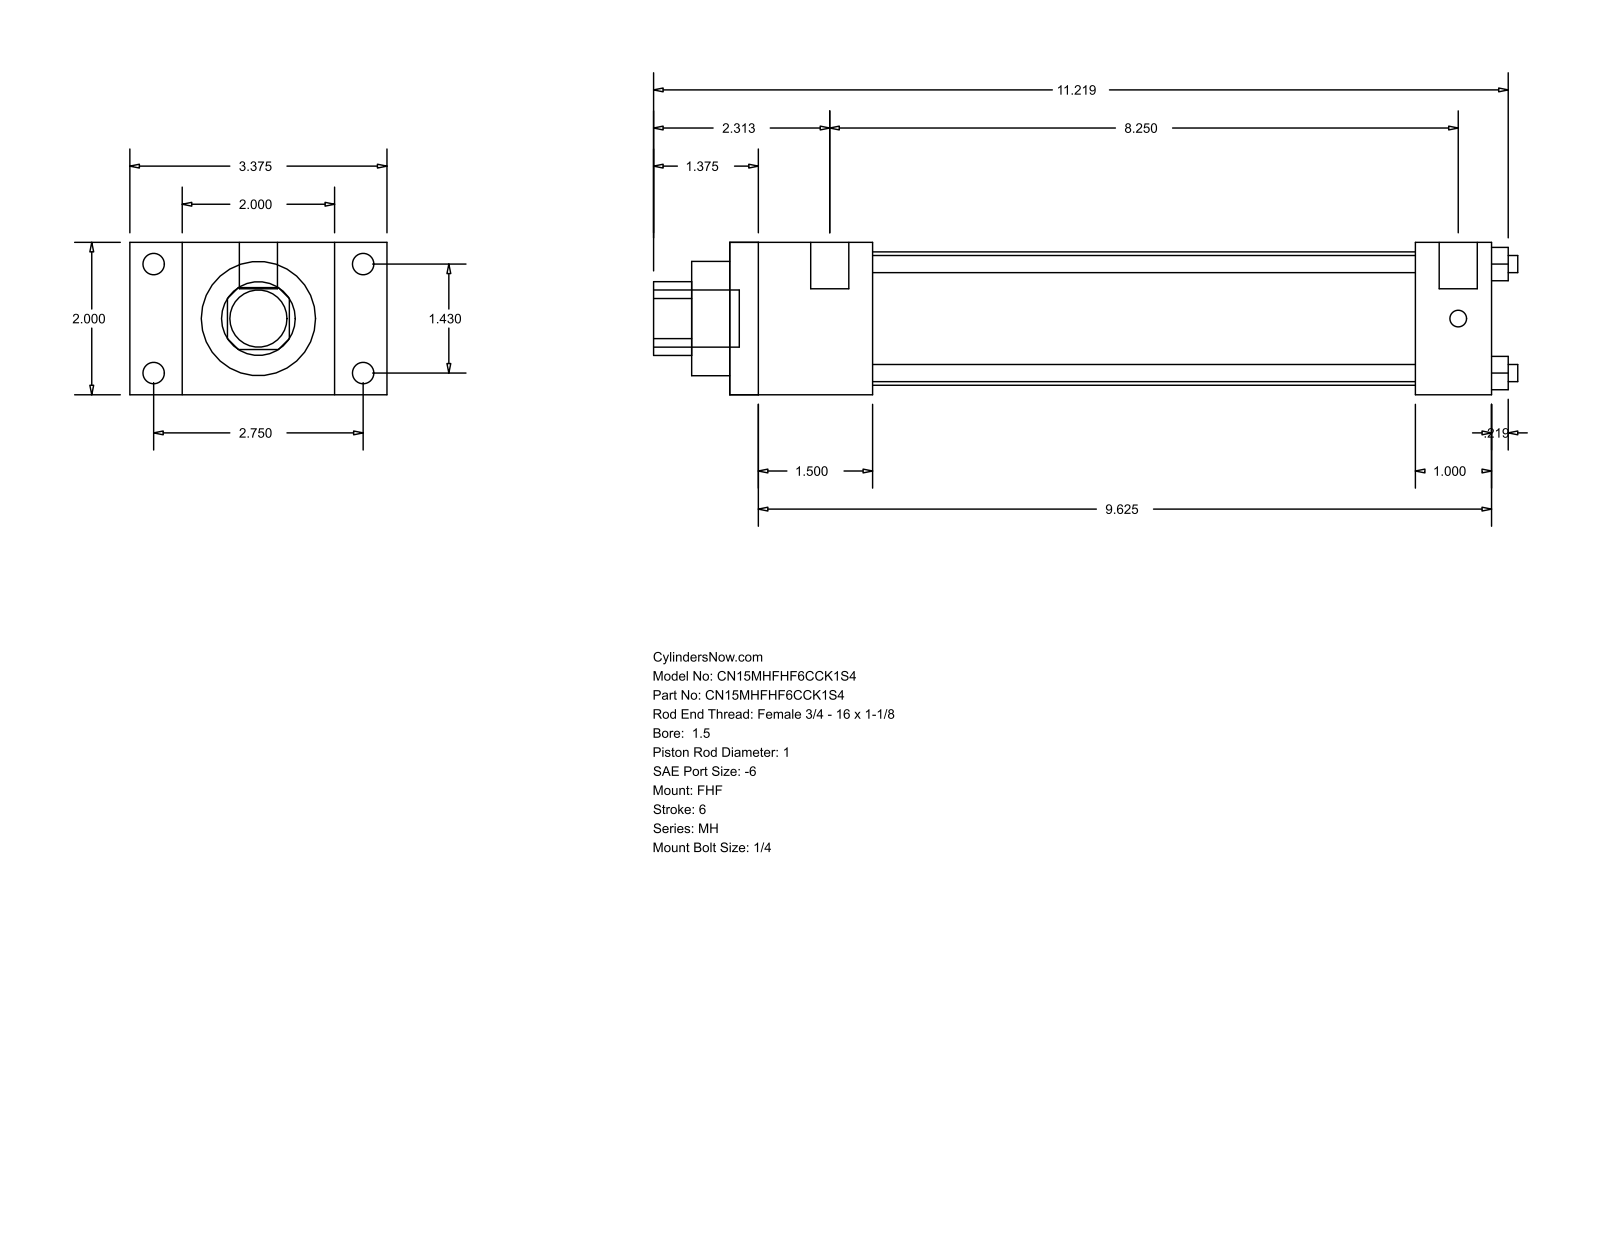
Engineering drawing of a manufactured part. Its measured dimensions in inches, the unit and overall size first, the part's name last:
Units: inches
Overall size (bounding box): 11.344 × 3.375 × 2
Round holes (diameter × count): ⌀0.225 ×4, ⌀1 ×1, ⌀1.5 ×1, ⌀1.75 ×1
Round bosses / shafts (diameter × count): ⌀0.281 ×4, ⌀0.219 ×4, ⌀0.5 ×2, ⌀0.75 ×1
Partial cylindrical surfaces — rounded edges, fillets, slot ends (radius × count): R0.484 ×1
Main face-to-face distances: 2, 0.687, 2.687, 1.875, 3.375, 10, 8.125, 1, 9, 7.125
Hole centre spacings: 1.011, 1.43, 2.022
Bodies: 0 solids, 88 faces (60 planar, 28 cylindrical, 0 other)
Part name (STEP PRODUCT): MH_FHF__0150_1
STEP written by: GSSL Pune (CONFIG_CONTROL_DESIGN)
